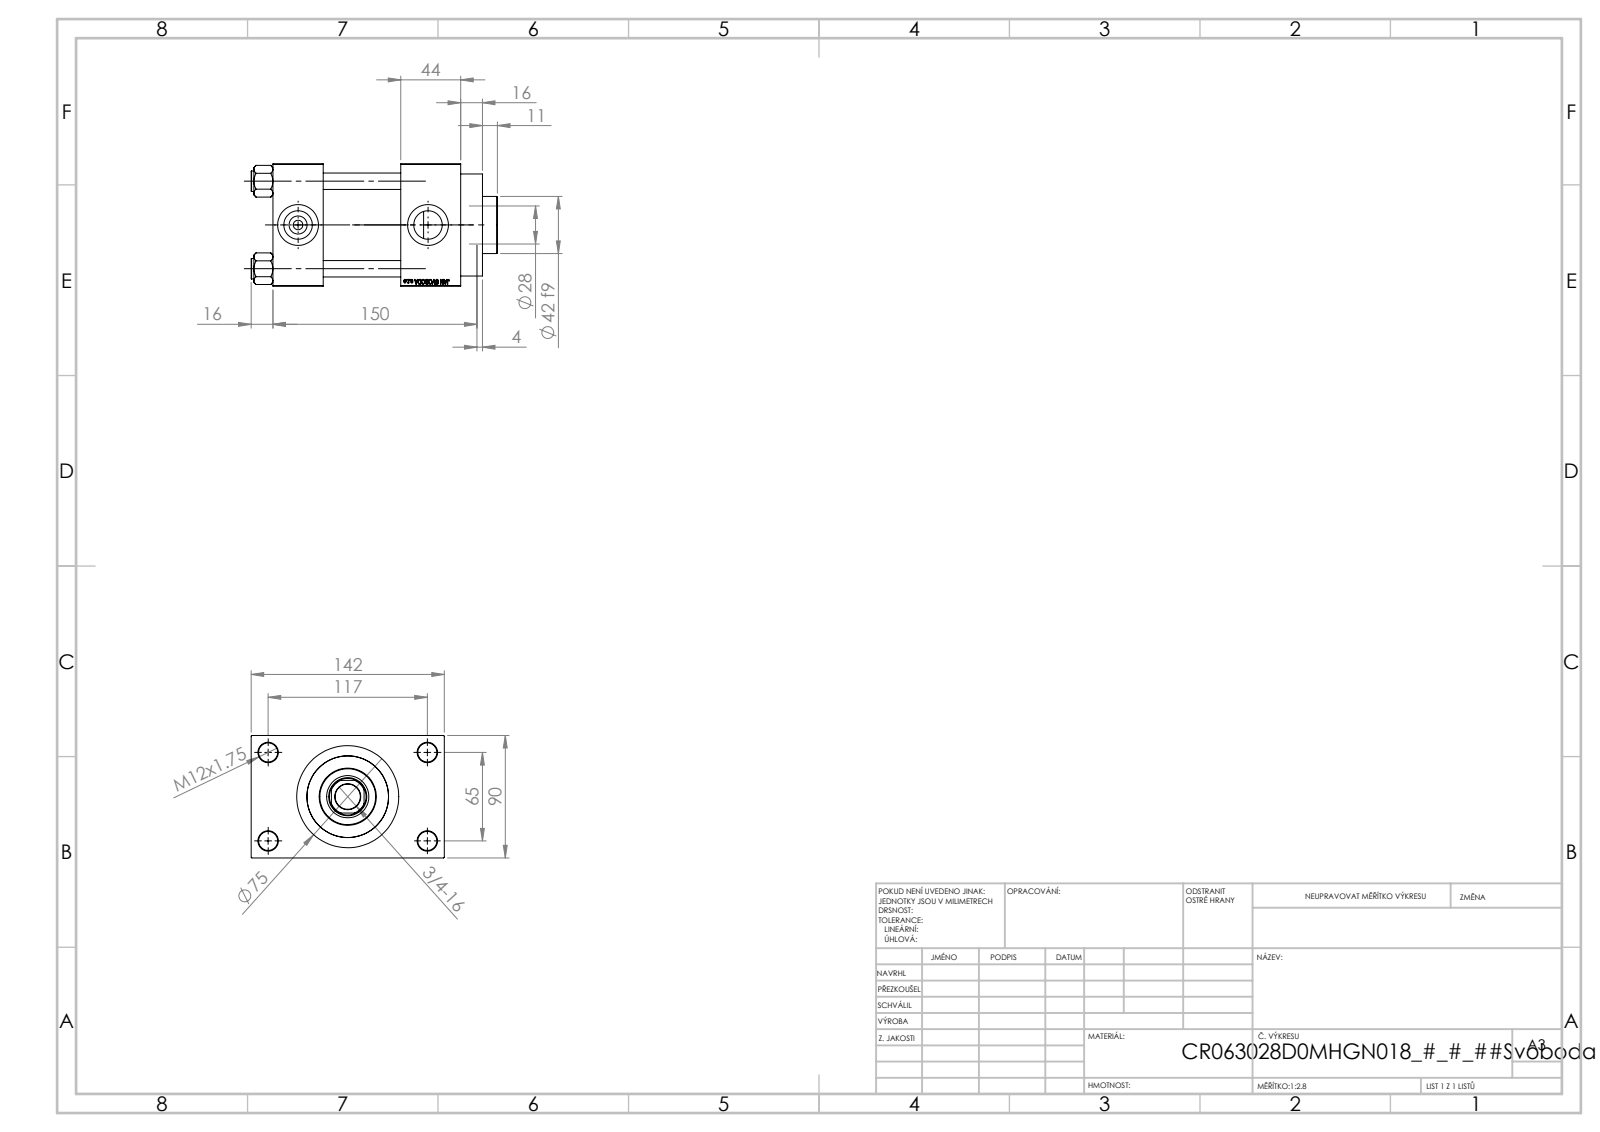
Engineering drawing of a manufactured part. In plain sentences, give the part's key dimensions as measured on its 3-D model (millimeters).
The part is named "V215_VC_A; V215CR_D_Body; V215CR_D_TYCINKA; NUT_M5_D (+1 more)". Its 3-D file was written by "SolidWorks 2019 (CONFIG_CONTROL_DESIGN)". It is 11 solids with 1103 faces: 497 planar, 88 cylindrical and 518 other. Overall it measures 181 by 142 by 90 millimeters. Its volume is 1 041 000 cubic millimeters and its surface area 194 608 square millimeters. Round holes: 4 of diameter 12, 4 of diameter 14, 2 of diameter 7, 2 of diameter 20.96, 2 of diameter 30, 1 of diameter 18.5, 1 of diameter 28, 1 of diameter 31, 1 of diameter 50, 1 of diameter 60, 1 of diameter 63. Round bosses or shafts: 4 of diameter 15, 1 of diameter 75, 1 of diameter 69, 1 of diameter 42. Partial cylindrical surfaces (rounded edges, fillets, slot ends): 1 of radius 13.5. The main face-to-face distances are 90, 57, 37, 94, 101, 138, 44, 26, 116, 16. The hole center spacings are 26.35, 45.47, 64.3, 66.92, 69.81, 90.65, 111.34, 65.
